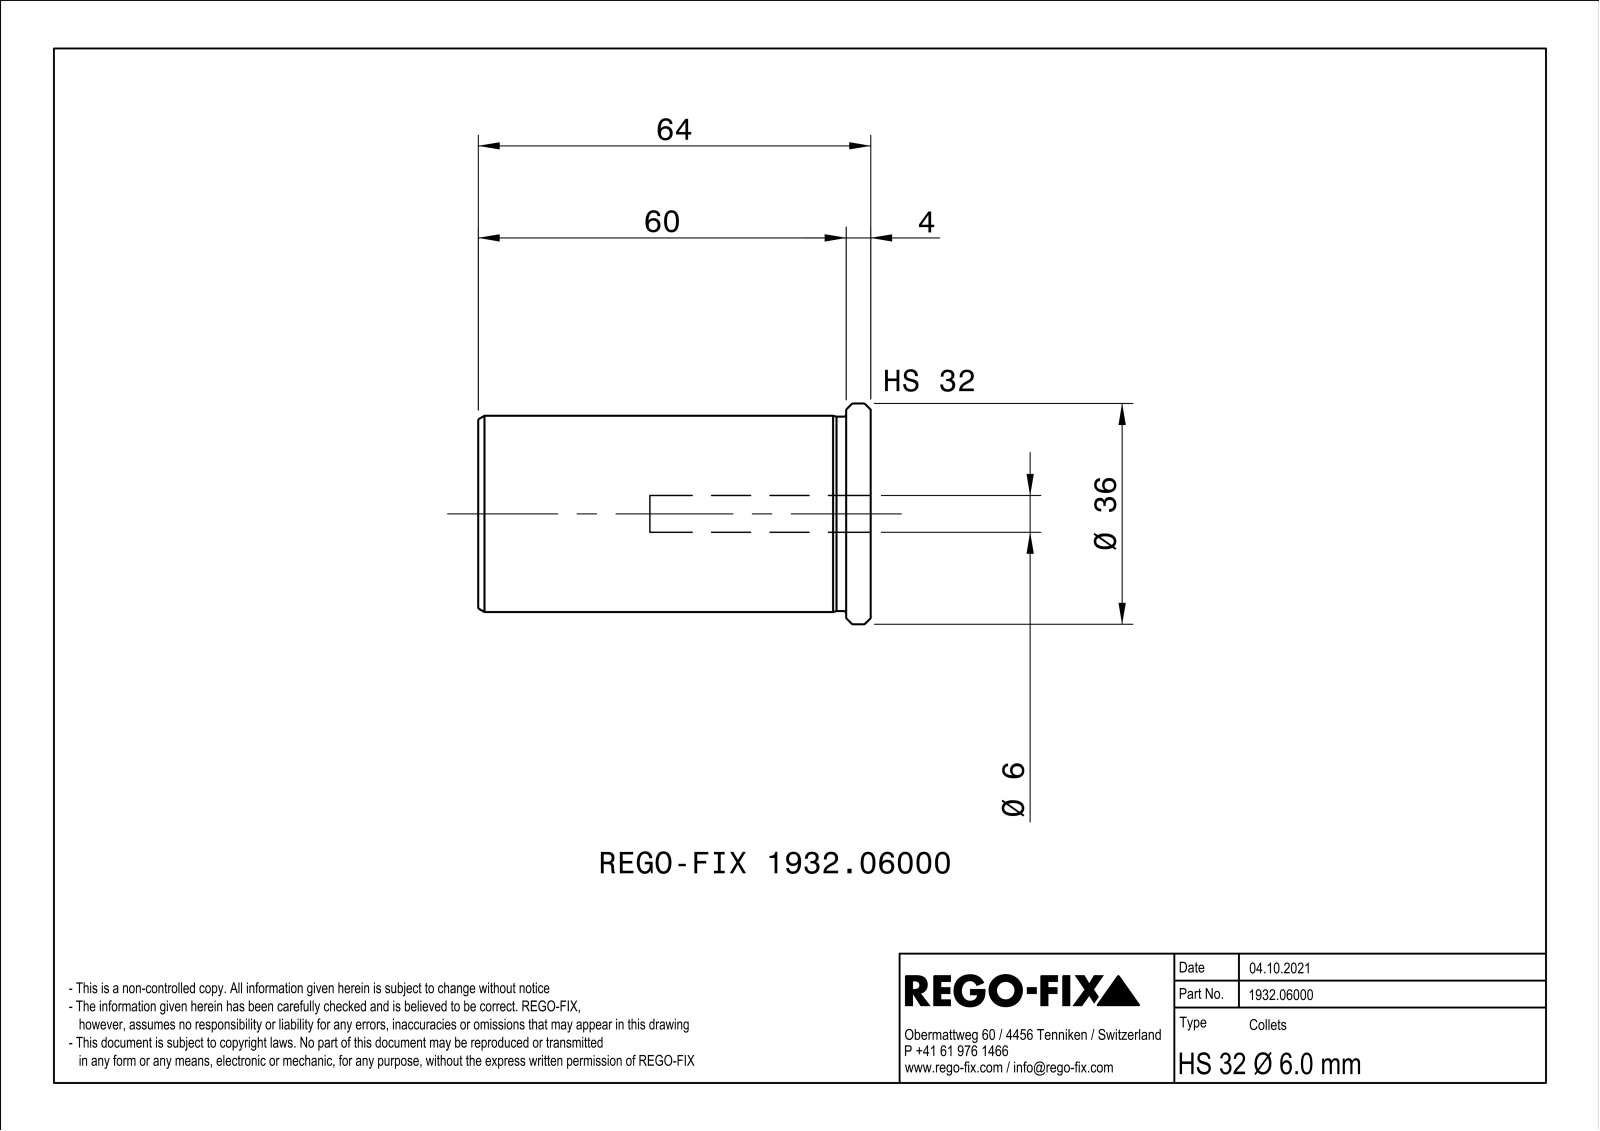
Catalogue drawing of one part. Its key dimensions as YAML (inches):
part_name: "NOCUT"
step_written_by: "SIEMENS PLM Software Solid Edge ST10 (AUTOMOTIVE_DESIGN)"
units: inches
bodies: {solids: 1, faces: 73, planar: 22, cylindrical: 12, other: 39}
overall_size: [2.52, 1.417, 1.417]
volume: 2.434
surface_area: 21.35
round_holes:
  - {diameter: 0.236, count: 1}
  - {diameter: 0.394, count: 1}
  - {diameter: 1.043, count: 1}
round_bosses_or_shafts:
  - {diameter: 1.417, count: 1}
  - {diameter: 1.26, count: 1}
  - {diameter: 1.248, count: 1}
face_to_face_distances: [0.039, 2.52, 0.157, 2.362]
